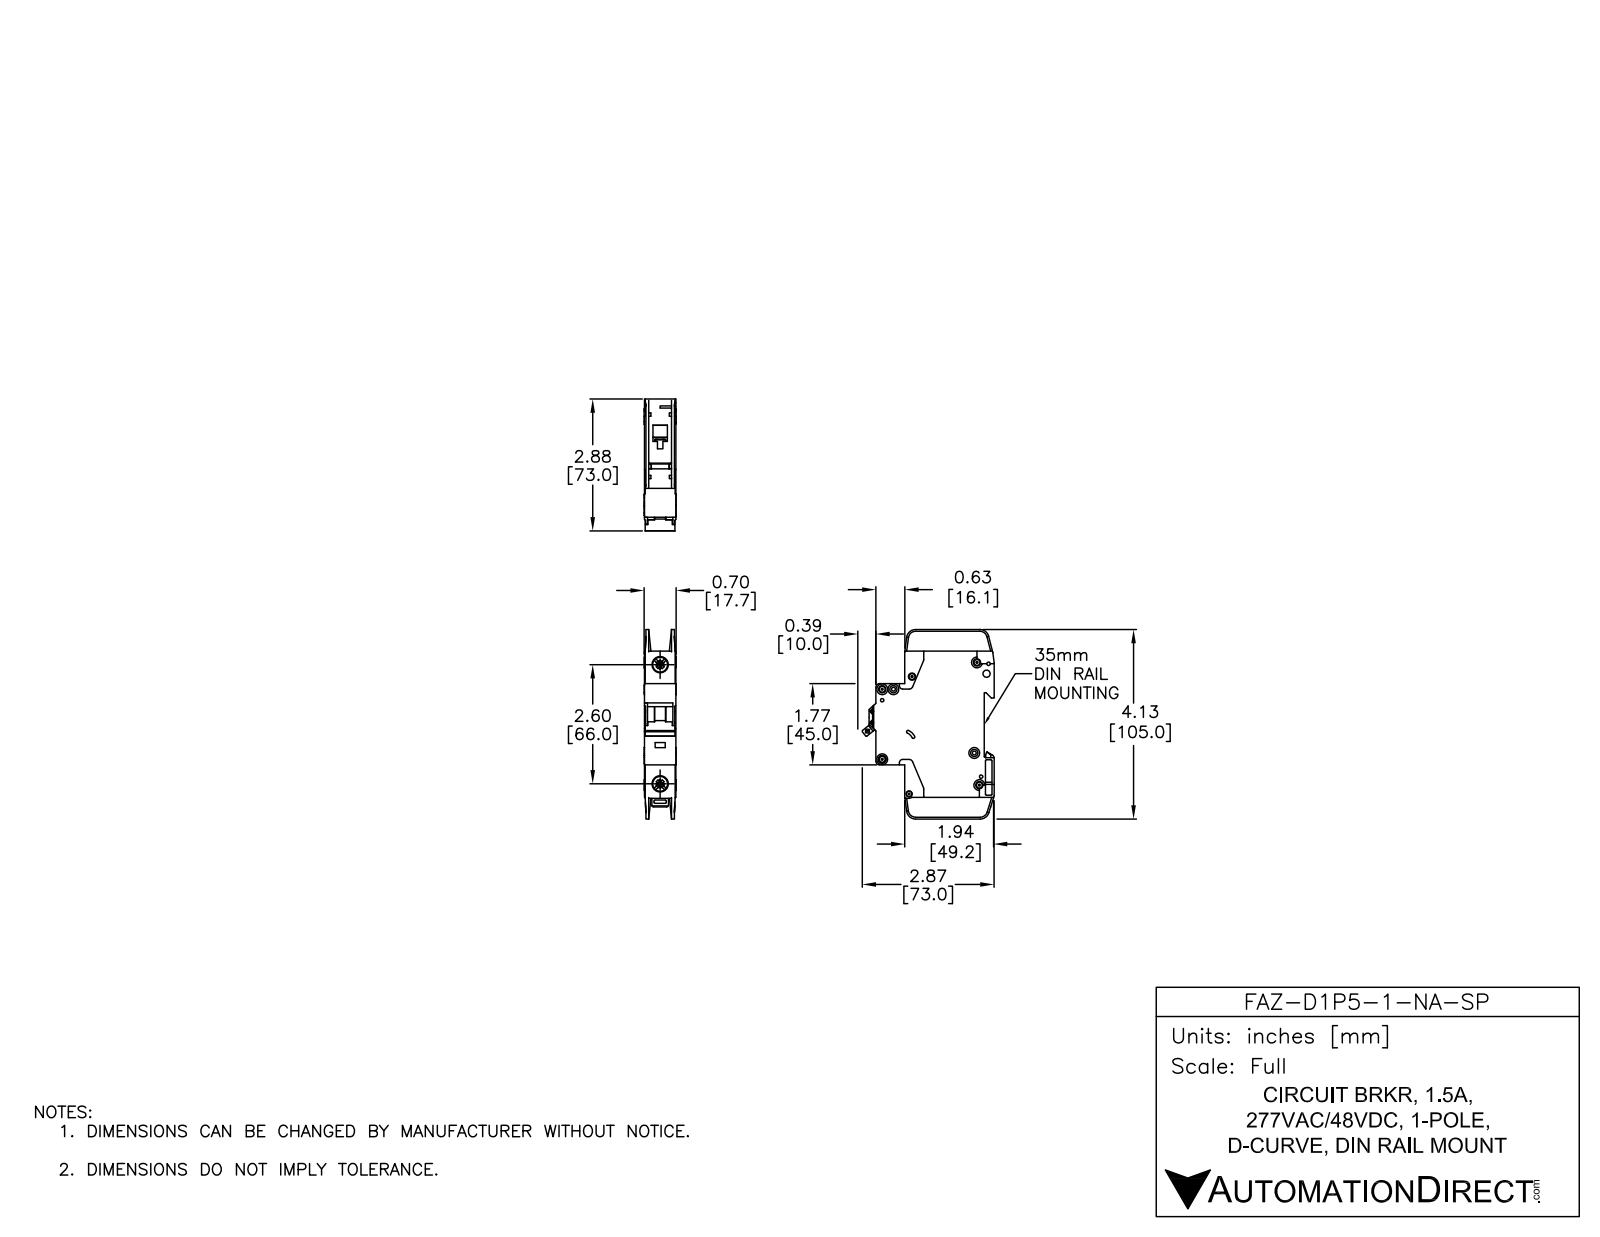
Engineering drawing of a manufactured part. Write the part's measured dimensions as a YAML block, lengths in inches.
part_name: "FAZ-D1P5-1-NA-SP"
step_written_by: "SolidWorks 2014 (AUTOMOTIVE_DESIGN)"
units: inches
bodies: {solids: 3, faces: 784, planar: 409, cylindrical: 263, other: 112}
overall_size: [4.134, 2.876, 0.697]
volume: 4.741
surface_area: 38.35
round_holes:
  - {diameter: 0.142, count: 7}
  - {diameter: 0.043, count: 2}
  - {diameter: 0.059, count: 2}
  - {diameter: 0.157, count: 2}
  - {diameter: 0.281, count: 2}
  - {diameter: 0.323, count: 2}
  - {diameter: 0.075, count: 1}
  - {diameter: 0.085, count: 1}
  - {diameter: 0.087, count: 1}
  - {diameter: 0.1, count: 1}
  - {diameter: 0.13, count: 1}
  - {diameter: 0.134, count: 1}
round_bosses_or_shafts:
  - {diameter: 0.236, count: 7}
  - {diameter: 0.098, count: 1}
partial_cylinders:
  - {radius: 0.01, count: 29}
  - {radius: 0.02, count: 18}
  - {radius: 0.039, count: 10}
  - {radius: 0.079, count: 10}
  - {radius: 0.197, count: 5}
  - {radius: 0.157, count: 4}
  - {radius: 0.071, count: 3}
  - {radius: 0.008, count: 2}
face_to_face_distances: [0.689, 0.593, 0.028, 0.096, 0.069, 0.62, 0.524, 0.551, 0.496, 0.079]
hole_center_spacings: [0.244, 0.204, 0.24, 0.322, 0.337, 0.343, 0.437, 0.49]
